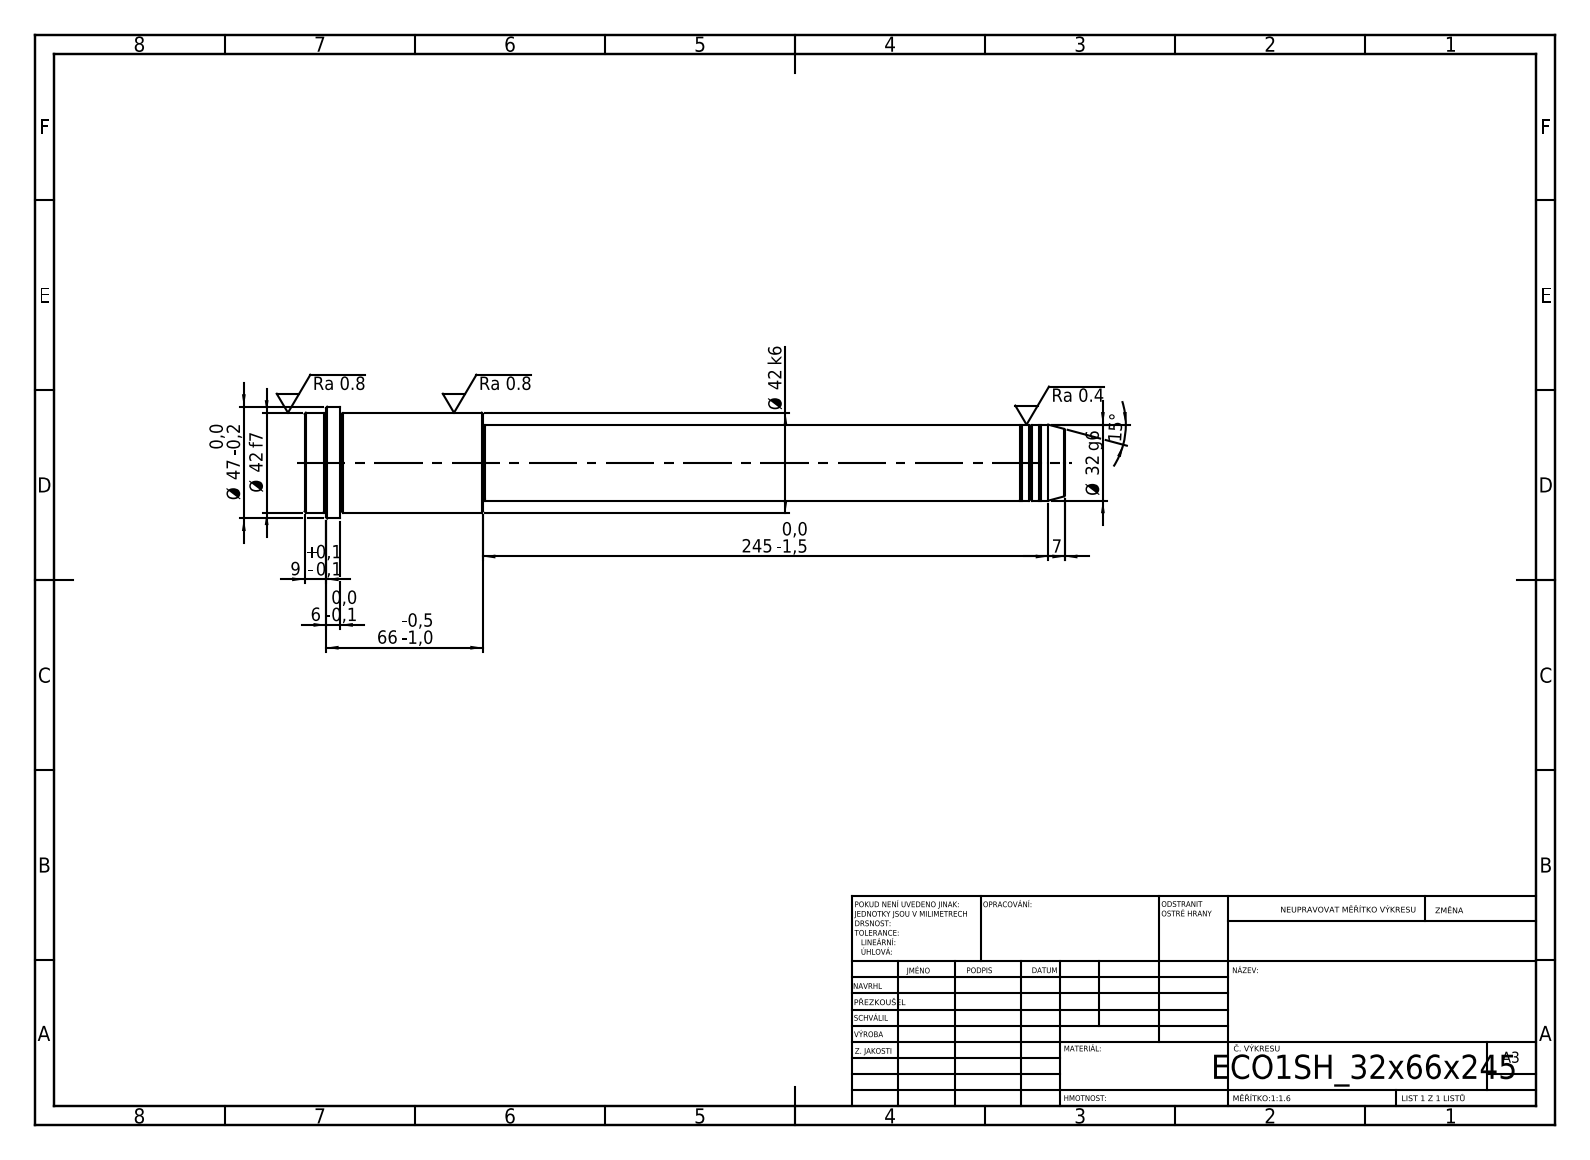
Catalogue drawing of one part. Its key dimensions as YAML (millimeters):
step_written_by: "SolidWorks 2019 (CONFIG_CONTROL_DESIGN)"
units: millimeters
bodies: {solids: 1, faces: 52, planar: 6, cylindrical: 16, other: 30}
overall_size: [320, 47, 47]
volume: 302089
surface_area: 38166
round_bosses_or_shafts:
  - {diameter: 47, count: 1}
  - {diameter: 42, count: 1}
  - {diameter: 32, count: 1}
  - {diameter: 31, count: 1}
face_to_face_distances: [320, 245, 75, 305, 60, 15, 311, 66, 6, 9]
